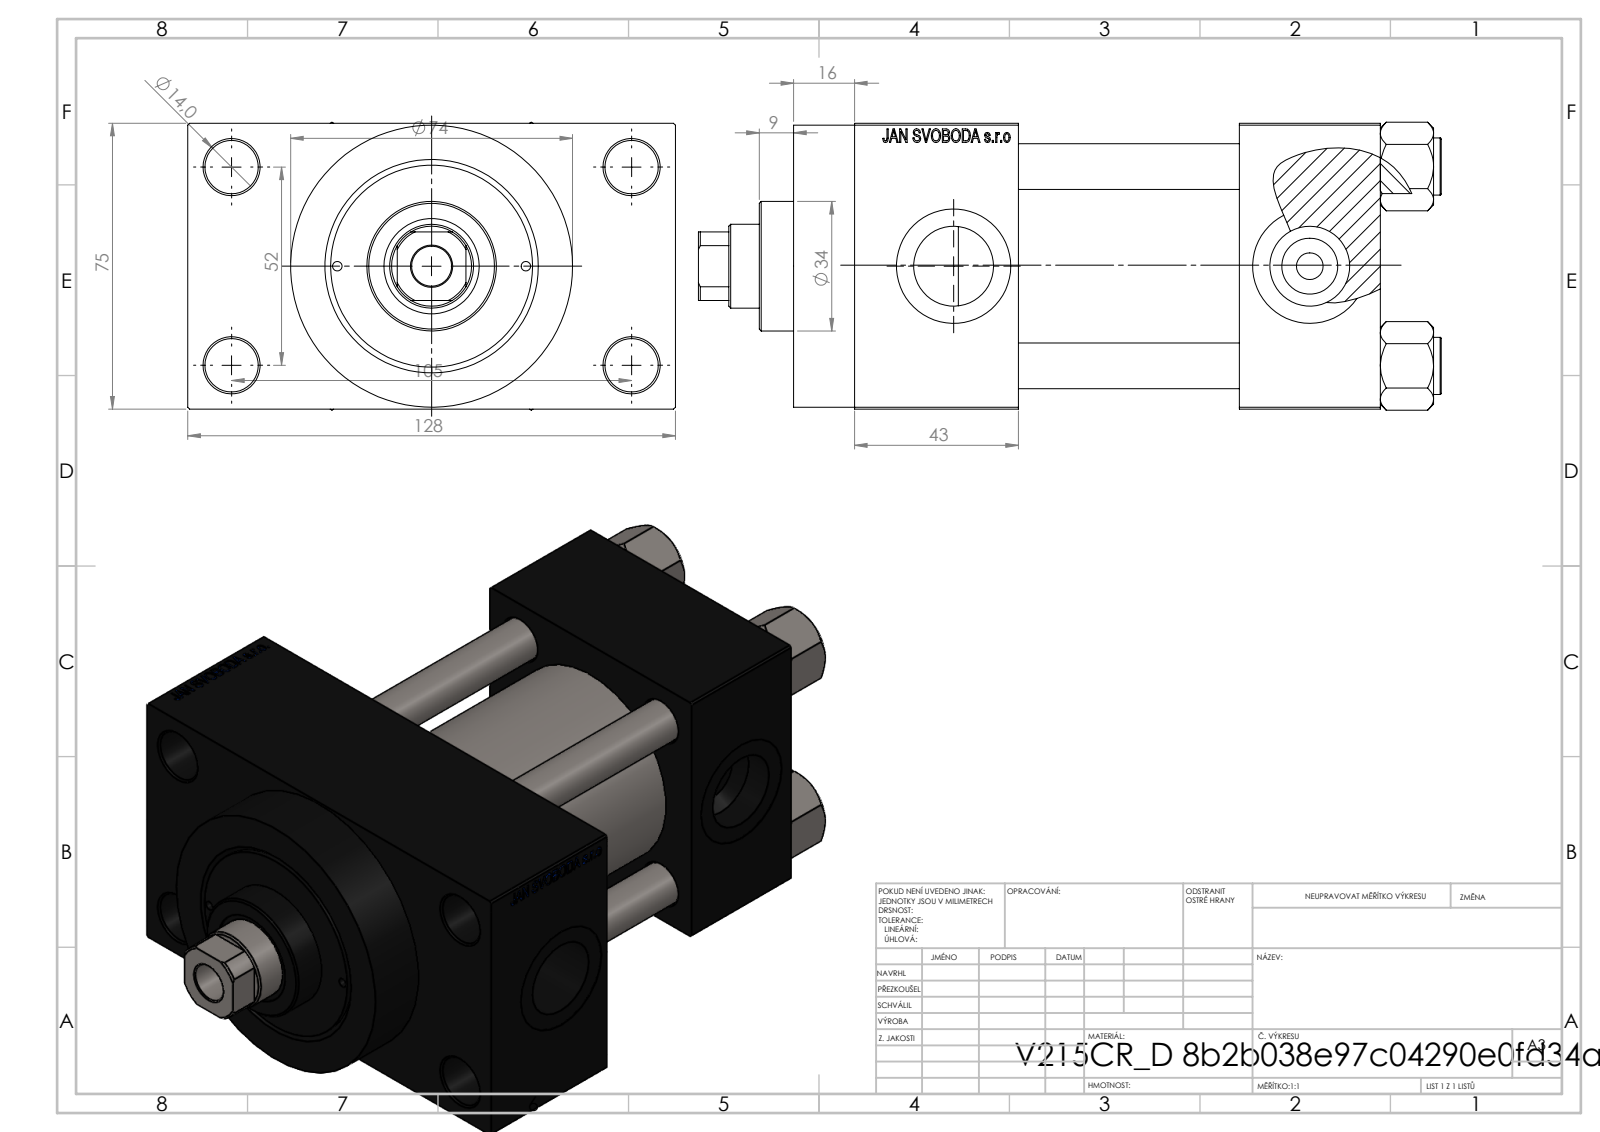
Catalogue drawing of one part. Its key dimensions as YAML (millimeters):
part_name: "V215CR_VCP_D; V215_VC_A; NUT_M5_D; V215CR_D_Body (+1 more)"
step_written_by: "SolidWorks 2019 (CONFIG_CONTROL_DESIGN)"
units: millimeters
bodies: {solids: 11, faces: 1111, planar: 499, cylindrical: 92, other: 520}
overall_size: [195, 128, 75.54]
volume: 797650
surface_area: 166512
round_holes:
  - {diameter: 12, count: 4}
  - {diameter: 14, count: 4}
  - {diameter: 2.5, count: 2}
  - {diameter: 7, count: 2}
  - {diameter: 20.96, count: 2}
  - {diameter: 30, count: 2}
  - {diameter: 10.5, count: 1}
  - {diameter: 22, count: 1}
  - {diameter: 25, count: 1}
  - {diameter: 41, count: 1}
  - {diameter: 50, count: 1}
  - {diameter: 53, count: 1}
round_bosses_or_shafts:
  - {diameter: 15, count: 4}
  - {diameter: 74, count: 1}
  - {diameter: 56, count: 1}
  - {diameter: 34, count: 1}
partial_cylinders:
  - {radius: 10.5, count: 1}
face_to_face_distances: [75, 58, 37, 95, 26.5, 138, 101, 43, 101.5, 16]
hole_center_spacings: [26.19, 26.35, 36.98, 38.03, 52.3, 57.22, 58.43, 58.59]
